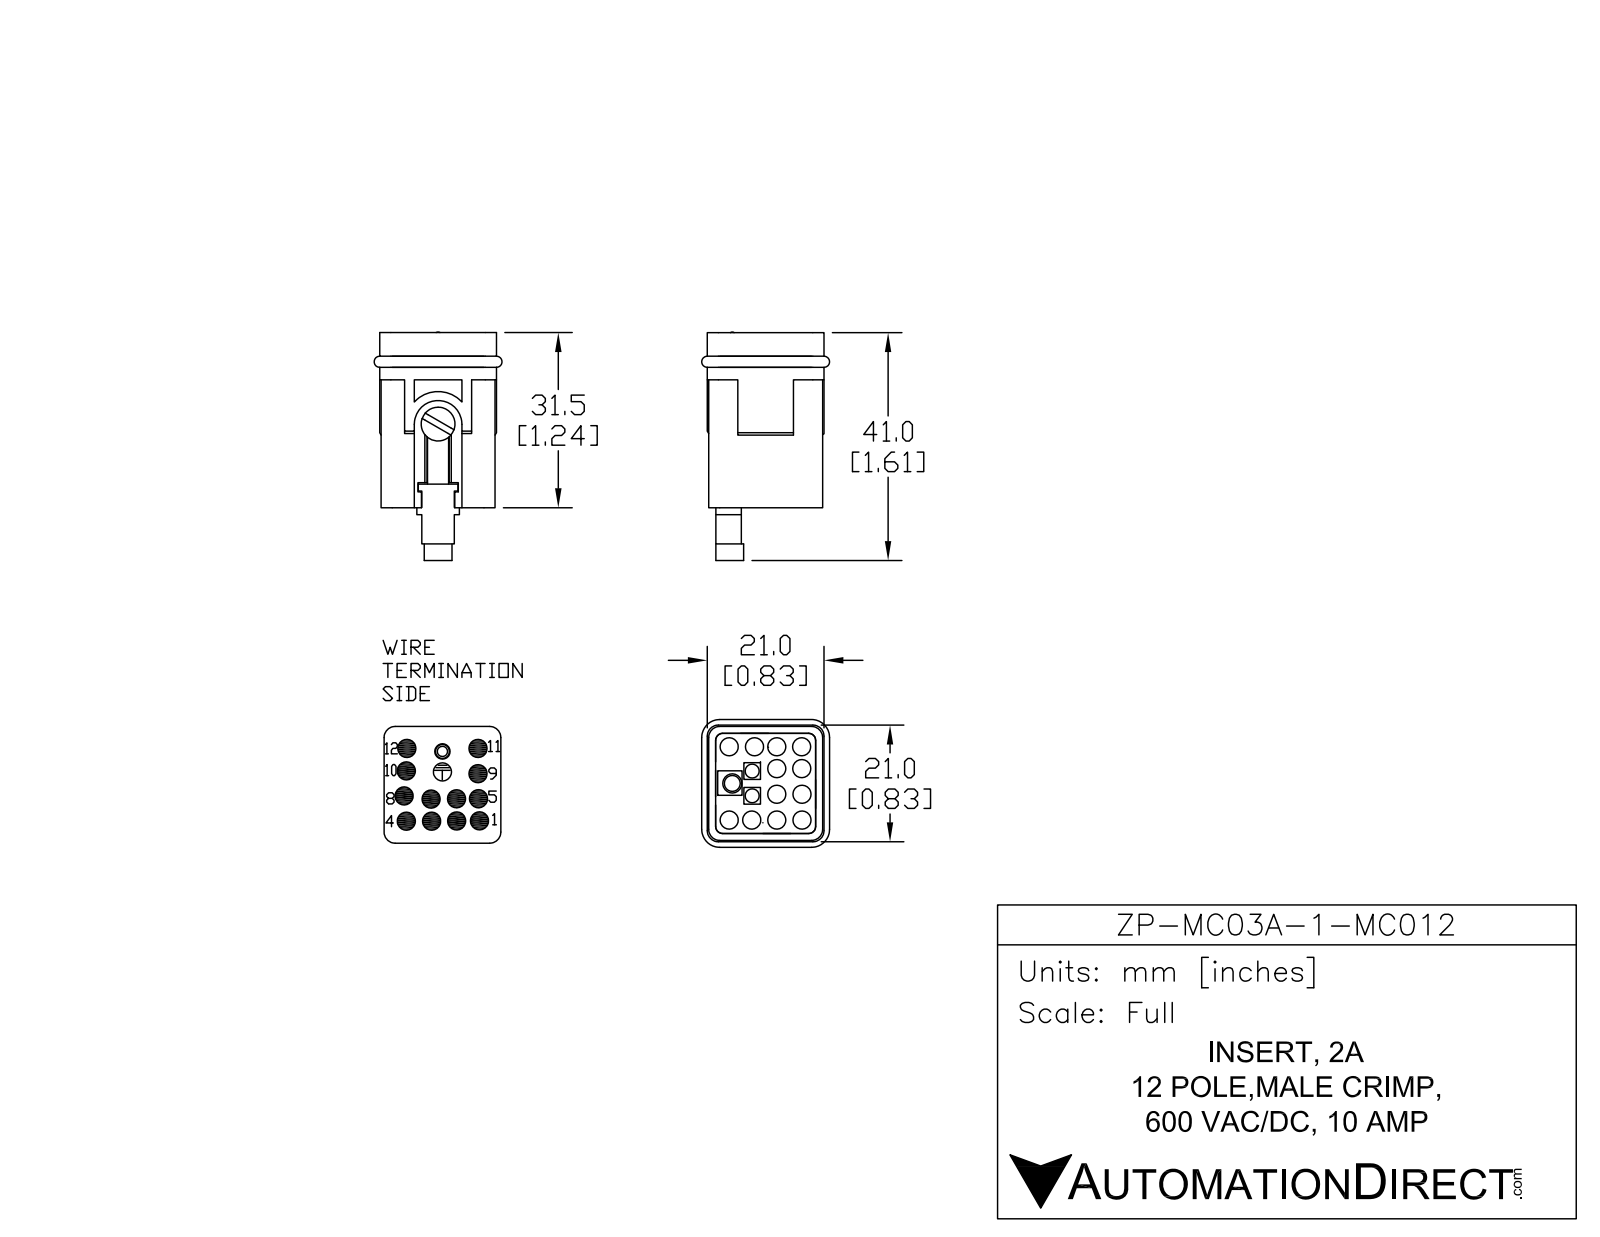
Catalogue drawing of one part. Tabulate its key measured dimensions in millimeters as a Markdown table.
| quantity | value |
| --- | --- |
| part name | ZP-MC03A-1-MC012 |
| STEP written by | SolidWorks 2014 (AUTOMOTIVE_DESIGN) |
| units | millimeters |
| bodies | 7 solids, 277 faces (172 planar, 89 cylindrical, 16 other) |
| overall size | 41.1 × 23 × 23 |
| volume | 7 390 mm³ |
| surface area | 8 975 mm² |
| round holes (diameter × count) | 3.25 × 12, 2.5 × 2, 1.56 × 1, 3.64 × 1, 3.75 × 1 |
| round bosses / shafts (diameter × count) | 2 × 4, 5.01 × 1, 4 × 1, 1.67 × 1, 1.3 × 1 |
| partial cylindrical surfaces (radius × count) | 2 × 13, 1.25 × 8, 1 × 2, 1.89 × 2, 2.5 × 2, 2 × 1, 2 × 1, 2.58 × 1 |
| main face-to-face distances | 1.25, 20.75, 1.5, 19.25, 19.5, 20.5, 21, 18, 3, 19.75 |
| hole center spacings | 4.61, 4.21, 4.56, 6.02, 6.44, 6.59, 6.61, 9.16 |
